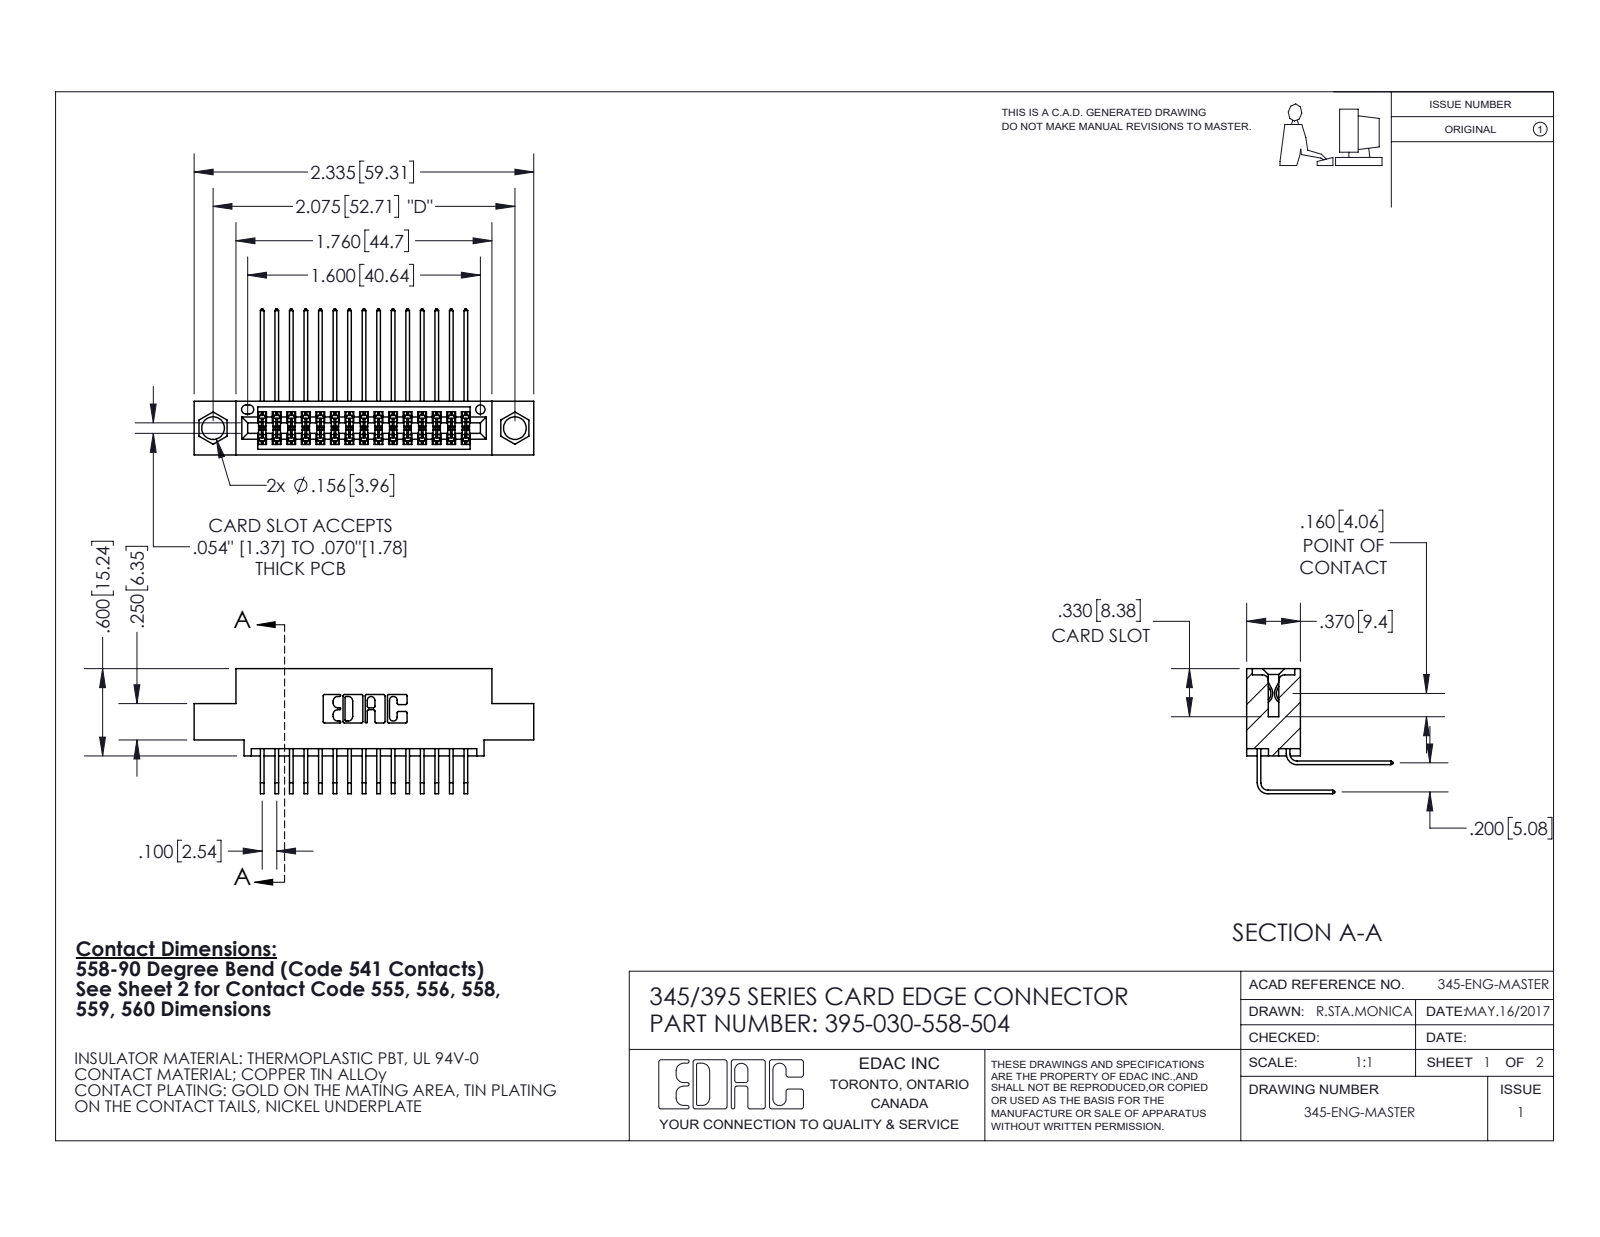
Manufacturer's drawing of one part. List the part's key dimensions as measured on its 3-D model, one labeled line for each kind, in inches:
Part name (STEP PRODUCT): 395-030-558-504; 345 Part_0.110 Offset - 0.156 Dia-TI; 345-292-001_558 559 Tail - 1; 345-292-001_558 Tail - 2
STEP written by: SolidWorks 2020 (CONFIG_CONTROL_DESIGN)
Units: inches
Bodies: 31 solids, 1704 faces (1148 planar, 556 cylindrical, 0 other)
Overall size (bounding box): 2.335 × 1.005 × 0.859
Volume: 0.336 in³ · Surface area: 12.98 in²
Round holes (diameter × count): ⌀0.156 ×2, ⌀0.064 ×1
Partial cylindrical surfaces — rounded edges, fillets, slot ends (radius × count): R0.006 ×60, R0.01 ×22, R0.007 ×6, R0.031 ×6, R0.026 ×3, R0.014 ×2, R0.019 ×2, R0.022 ×2
Main face-to-face distances: 0.2, 0.072, 0.298, 0.37, 0.098, 0.272, 0.025, 0.225, 0.1, 0.025
Hole centre spacings: 0.27, 1.842, 2.075
